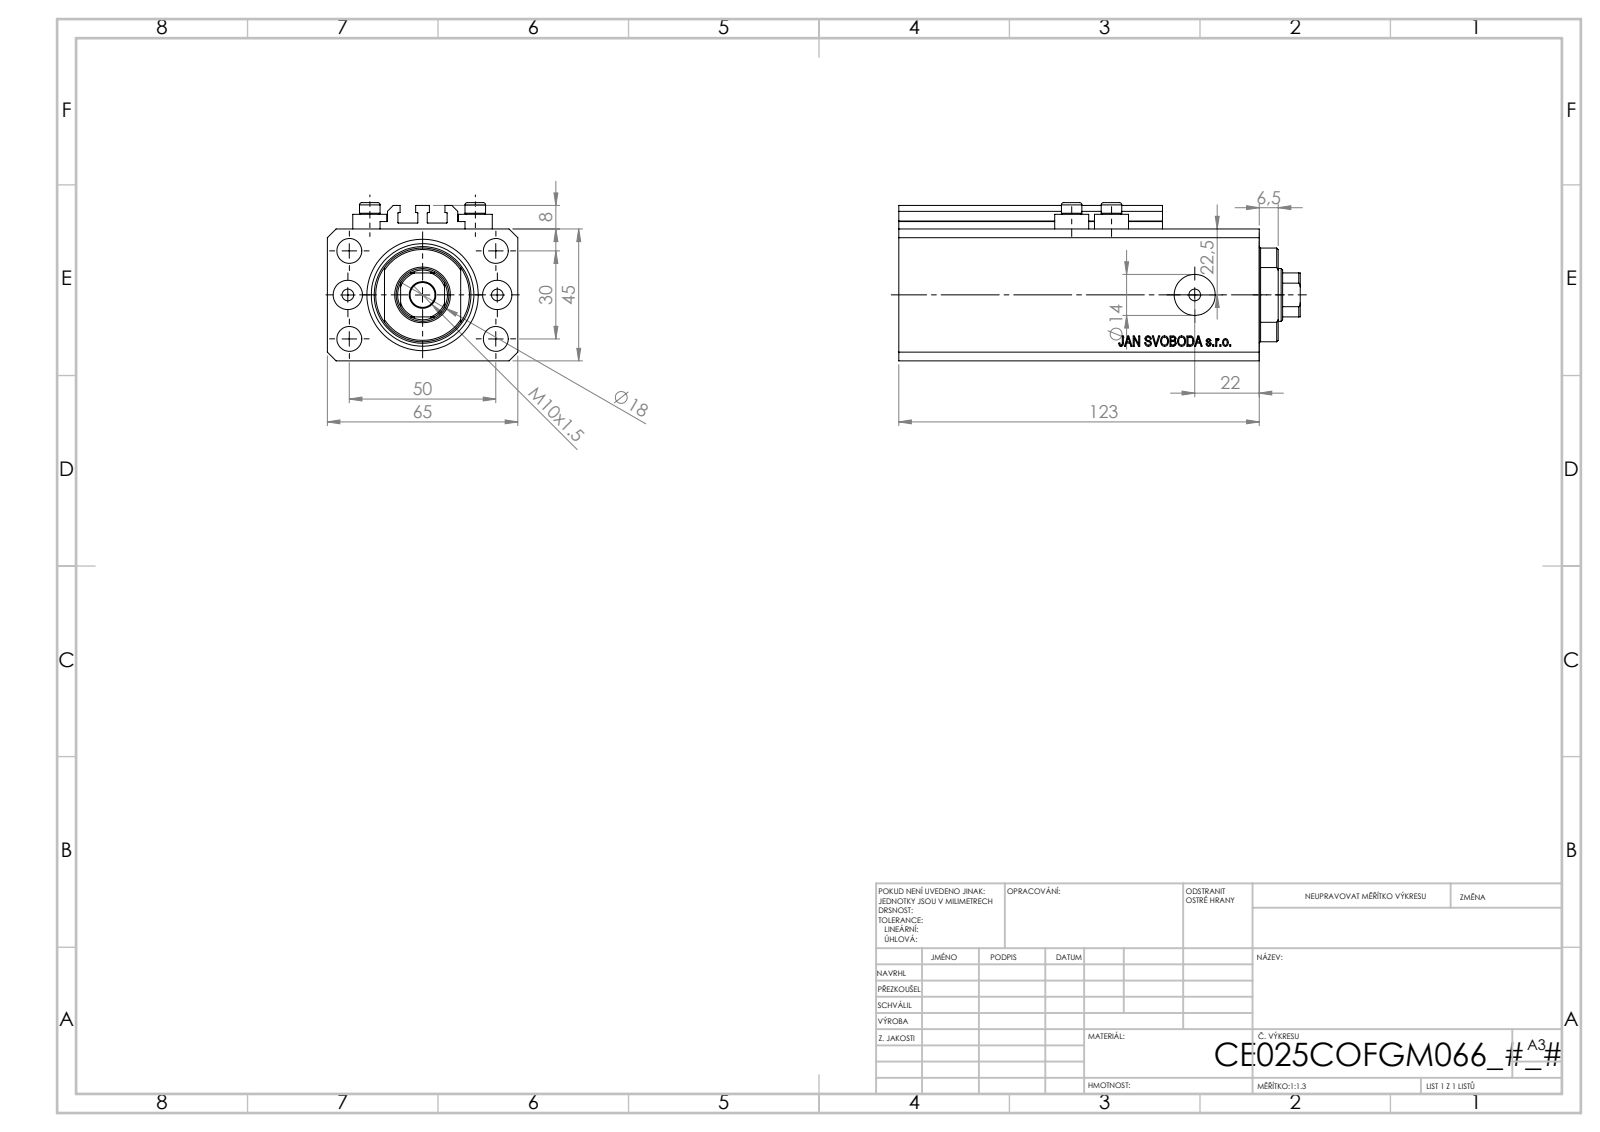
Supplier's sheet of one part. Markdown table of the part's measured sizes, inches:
| quantity | value |
| --- | --- |
| part name | ALLEN BOLT V250CE; V250CE_C_VCP; V250CE_C_Body; V250CE_VC_C |
| STEP written by | SolidWorks 2019 (CONFIG_CONTROL_DESIGN) |
| units | inches |
| bodies | 8 solids, 1034 faces (504 planar, 86 cylindrical, 444 other) |
| overall size | 5.394 × 2.559 × 2.126 |
| volume | 20.15 in³ |
| surface area | 128.4 in² |
| round holes (diameter × count) | 0.157 × 8, 0.335 × 5, 0.394 × 2, 0.551 × 2, 0.709 × 1, 0.984 × 1, 1.496 × 1 |
| round bosses / shafts (diameter × count) | 0.457 × 4, 0.276 × 4 |
| partial cylindrical surfaces (radius × count) | 0.008 × 10, 0.335 × 1, 0.63 × 1 |
| main face-to-face distances | 1.772, 2.559, 0.551, 1.85, 4.291, 4.843, 0.098, 0.394, 0.079, 0.807 |
| hole center spacings | 0.591, 1.148, 2.074, 0.535, 1.004, 1.181, 1.417, 1.515 |
